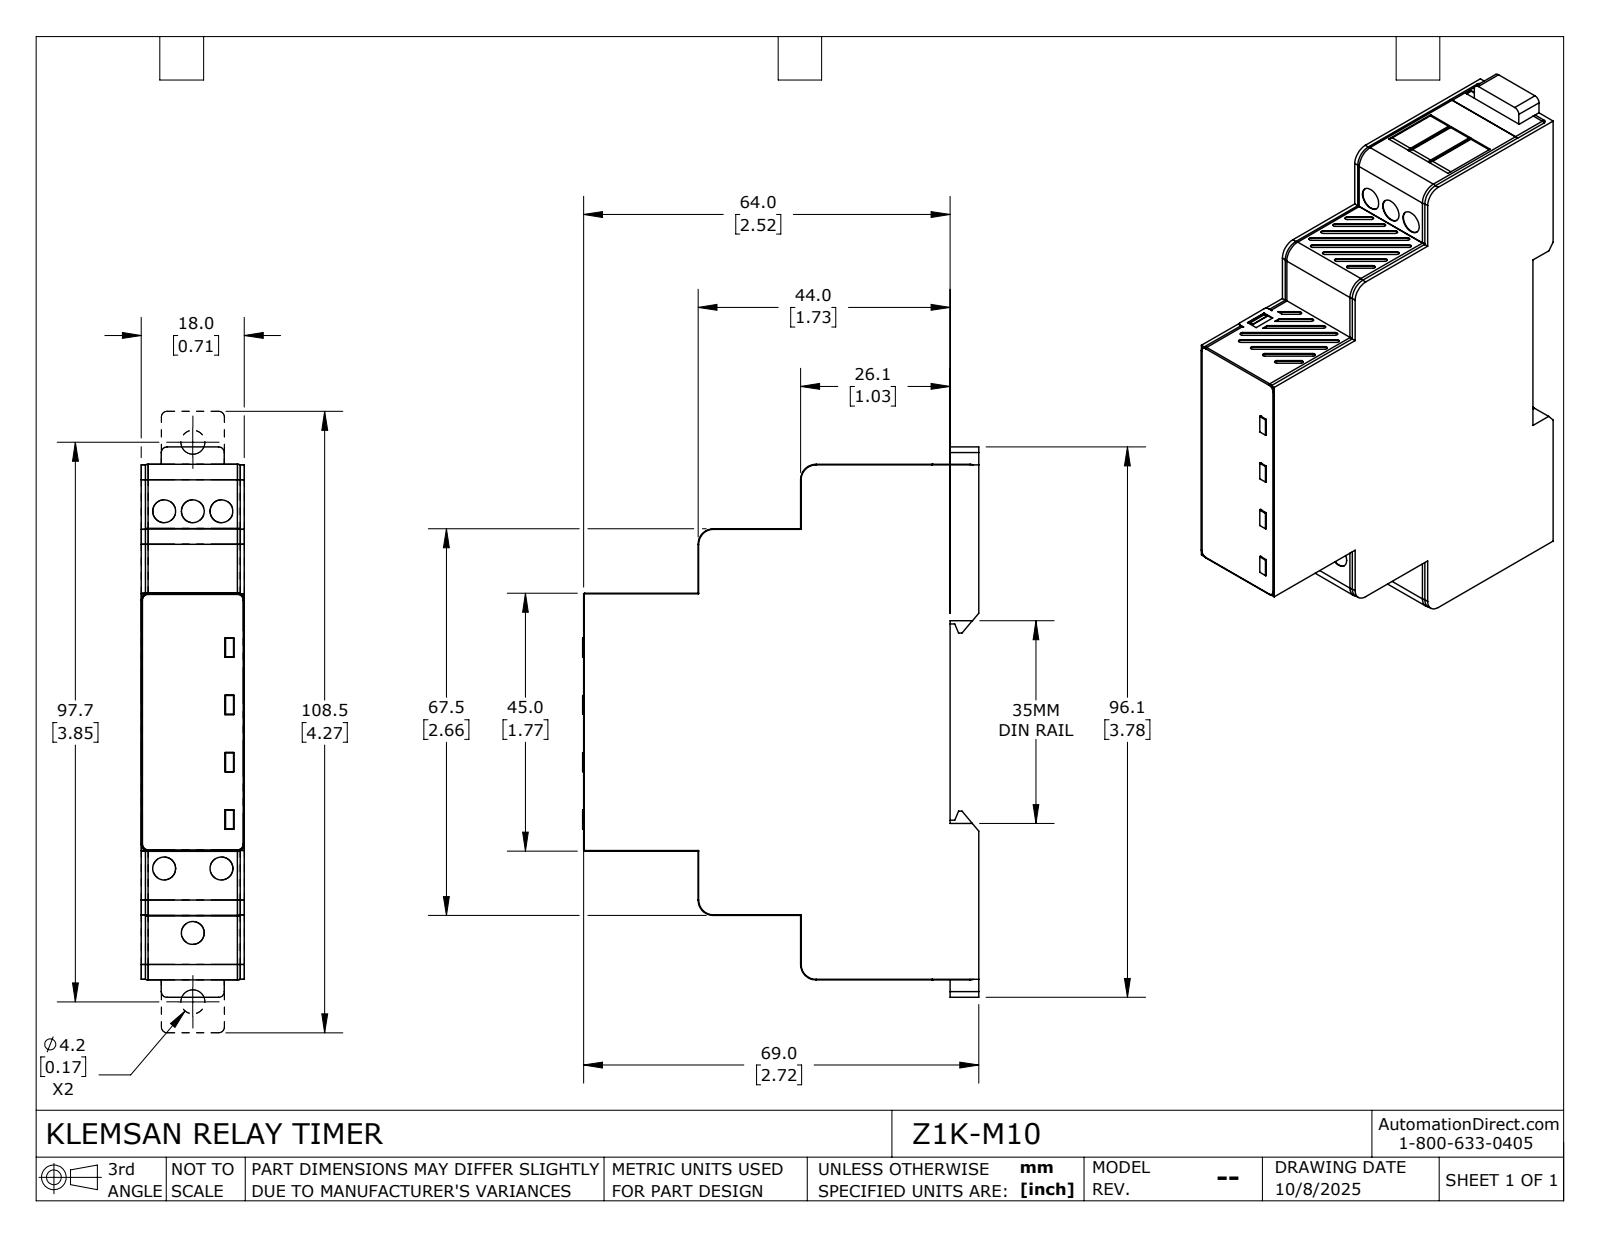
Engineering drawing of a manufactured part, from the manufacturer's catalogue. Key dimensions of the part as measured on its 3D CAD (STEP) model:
Part name (STEP PRODUCT): Z1K-M10
STEP written by: SolidWorks 2024 (CONFIG_CONTROL_DESIGN)
Units: millimetres
Bodies: 3 solids, 440 faces (280 planar, 60 cylindrical, 100 other)
Overall size (bounding box): 96.07 × 69.15 × 18
Volume: 83 847 mm³ · Surface area: 17 884 mm²
Round holes (diameter × count): ⌀4.2 ×2, ⌀4 ×1
Partial cylindrical surfaces — rounded edges, fillets, slot ends (radius × count): R1.2 ×16, R0.2 ×4, R1 ×4, R2.6 ×4, R2.7 ×4, R0.5 ×2, R1.5 ×2
Main face-to-face distances: 18, 3.5, 14.5, 11.25, 64, 5, 69, 22.5, 67.4, 67.5
Hole centre spacings: 5.83, 79.43, 85.26
